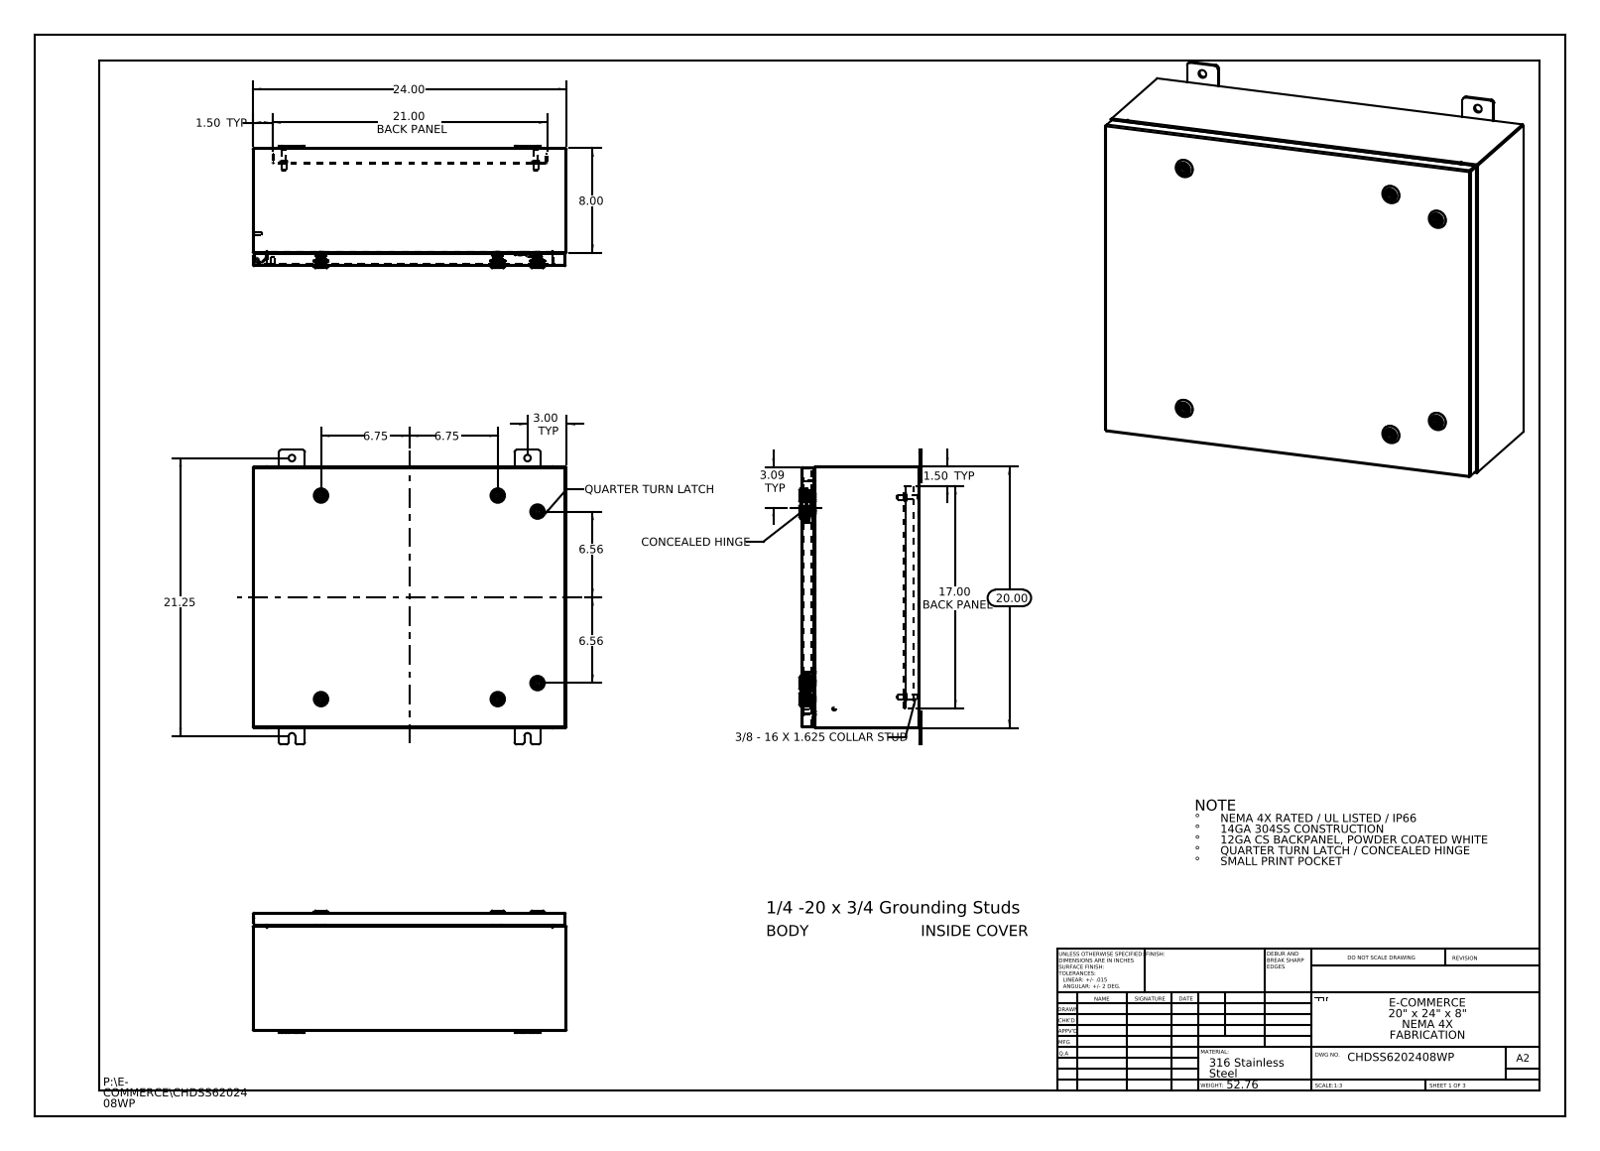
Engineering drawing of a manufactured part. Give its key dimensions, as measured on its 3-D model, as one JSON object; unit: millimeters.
{"part_name": "Housing-211301-IB-Industrilas_Housing-211301-IB-Industrilas; HW-CLH-E5-8004_Cam-232112-U-Industrilas; Insert-221320-IB-Industrilas_Insert-221320-IB-Industrilas; CHDSS6202408WP Mounting Feet (+8 more)", "step_written_by": "SolidWorks 2013 (CONFIG_CONTROL_DESIGN)", "units": "millimeters", "bodies": {"solids": 55, "faces": 5420, "planar": 1592, "cylindrical": 1692, "other": 2136}, "overall_size": [609.6, 571.5, 237.6], "volume_mm3": 3091000, "surface_area_mm2": 3044000, "round_holes": [[12.7, 8], [5, 6], [10, 6], [10.2, 6], [16, 6], [20, 6], [3.5, 4], [5.4, 1]], "round_bosses_or_shafts": [[6, 8], [28, 6], [19.8, 6], [15.9, 6], [15.5, 6], [13.5, 6], [10, 6], [2.9, 6]], "partial_cylinders_radius": [[0.2, 198], [3, 198], [0.7, 72], [0.5, 24], [4.8, 24], [5, 24], [0.3, 20], [2.2, 18]], "face_to_face_distances": [1.9, 1.9, 228.9, 226.9, 227, 225.1, 506.1, 2.6, 25.4, 27.3], "hole_center_spacings": [17.5, 47.2, 83.2, 342.9, 347.6, 387.4, 395, 421.2]}
